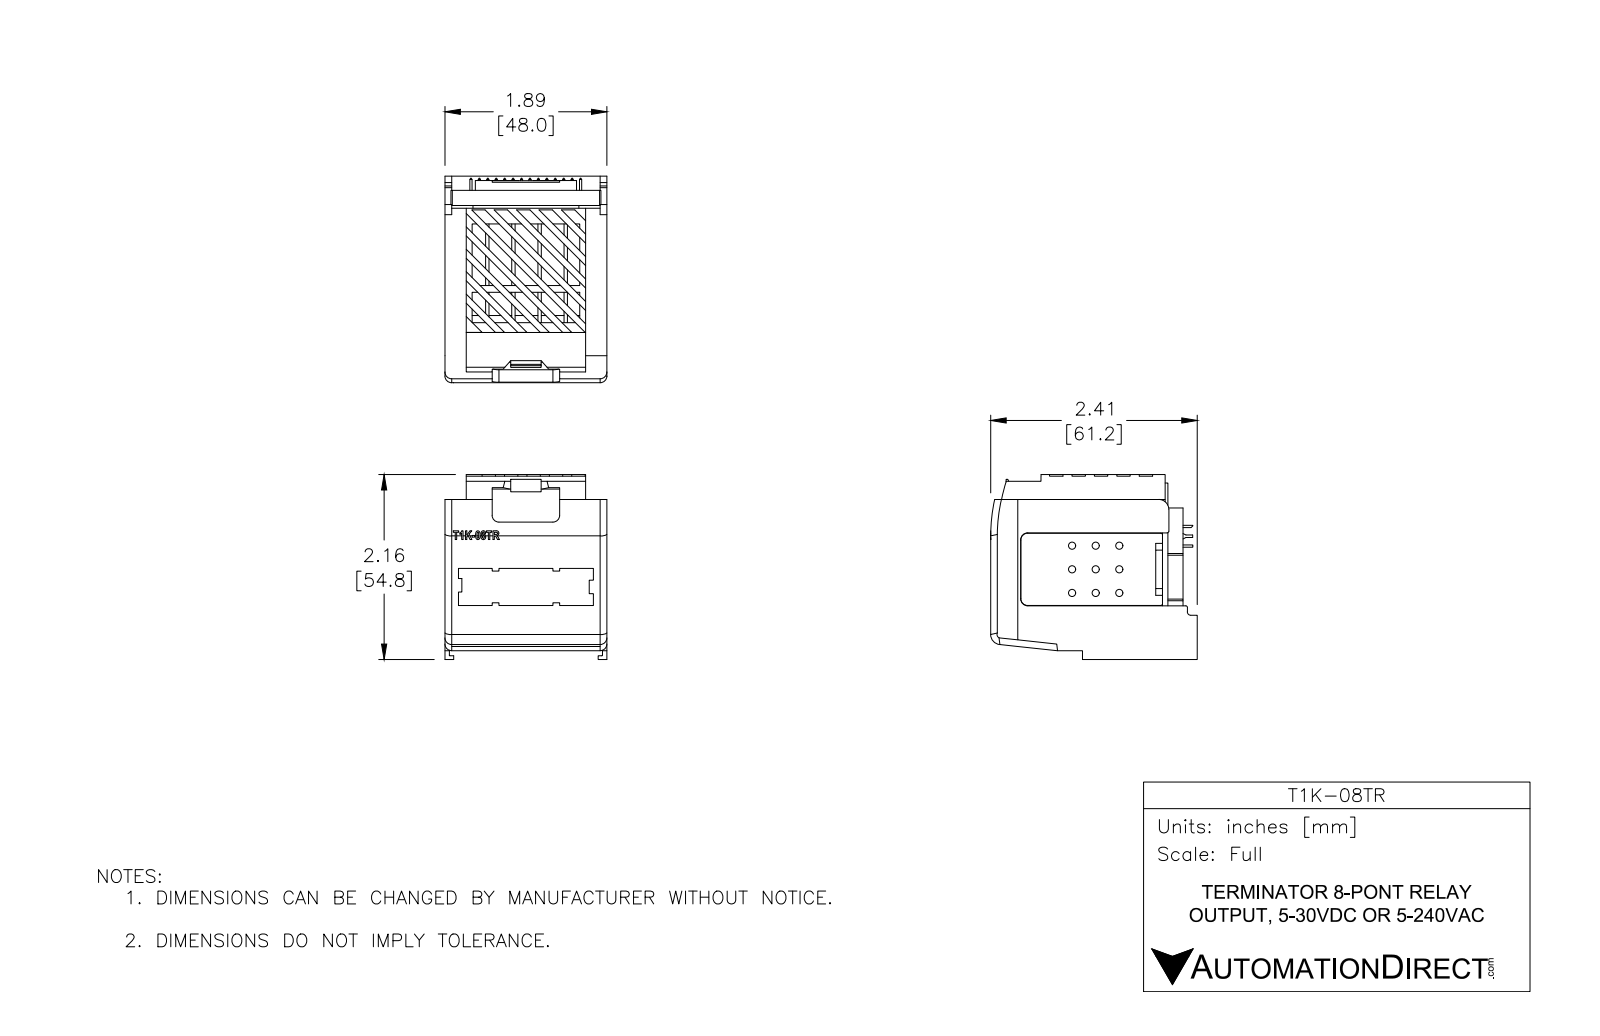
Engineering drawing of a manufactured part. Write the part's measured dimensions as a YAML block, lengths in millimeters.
part_name: "T1K-08TR"
step_written_by: "SolidWorks 2013 (AUTOMOTIVE_DESIGN)"
units: millimeters
bodies: {solids: 1, faces: 546, planar: 413, cylindrical: 101, other: 32}
overall_size: [65.1, 61.36, 47.6]
volume: 30279
surface_area: 35941
round_holes:
  - {diameter: 3, count: 8}
round_bosses_or_shafts:
  - {diameter: 0.7, count: 28}
partial_cylinders:
  - {radius: 3.5, count: 10}
  - {radius: 1, count: 5}
  - {radius: 0.25, count: 3}
  - {radius: 0.55, count: 3}
  - {radius: 1.5, count: 2}
  - {radius: 8, count: 1}
  - {radius: 10, count: 1}
  - {radius: 18, count: 1}
face_to_face_distances: [2, 45.6, 47.6, 43.6, 55.35, 49.9, 6.55, 39.05, 59.8, 9.9]
hole_center_spacings: [5.2, 10.4, 15.6, 20.8, 26, 31.2, 36.4]
